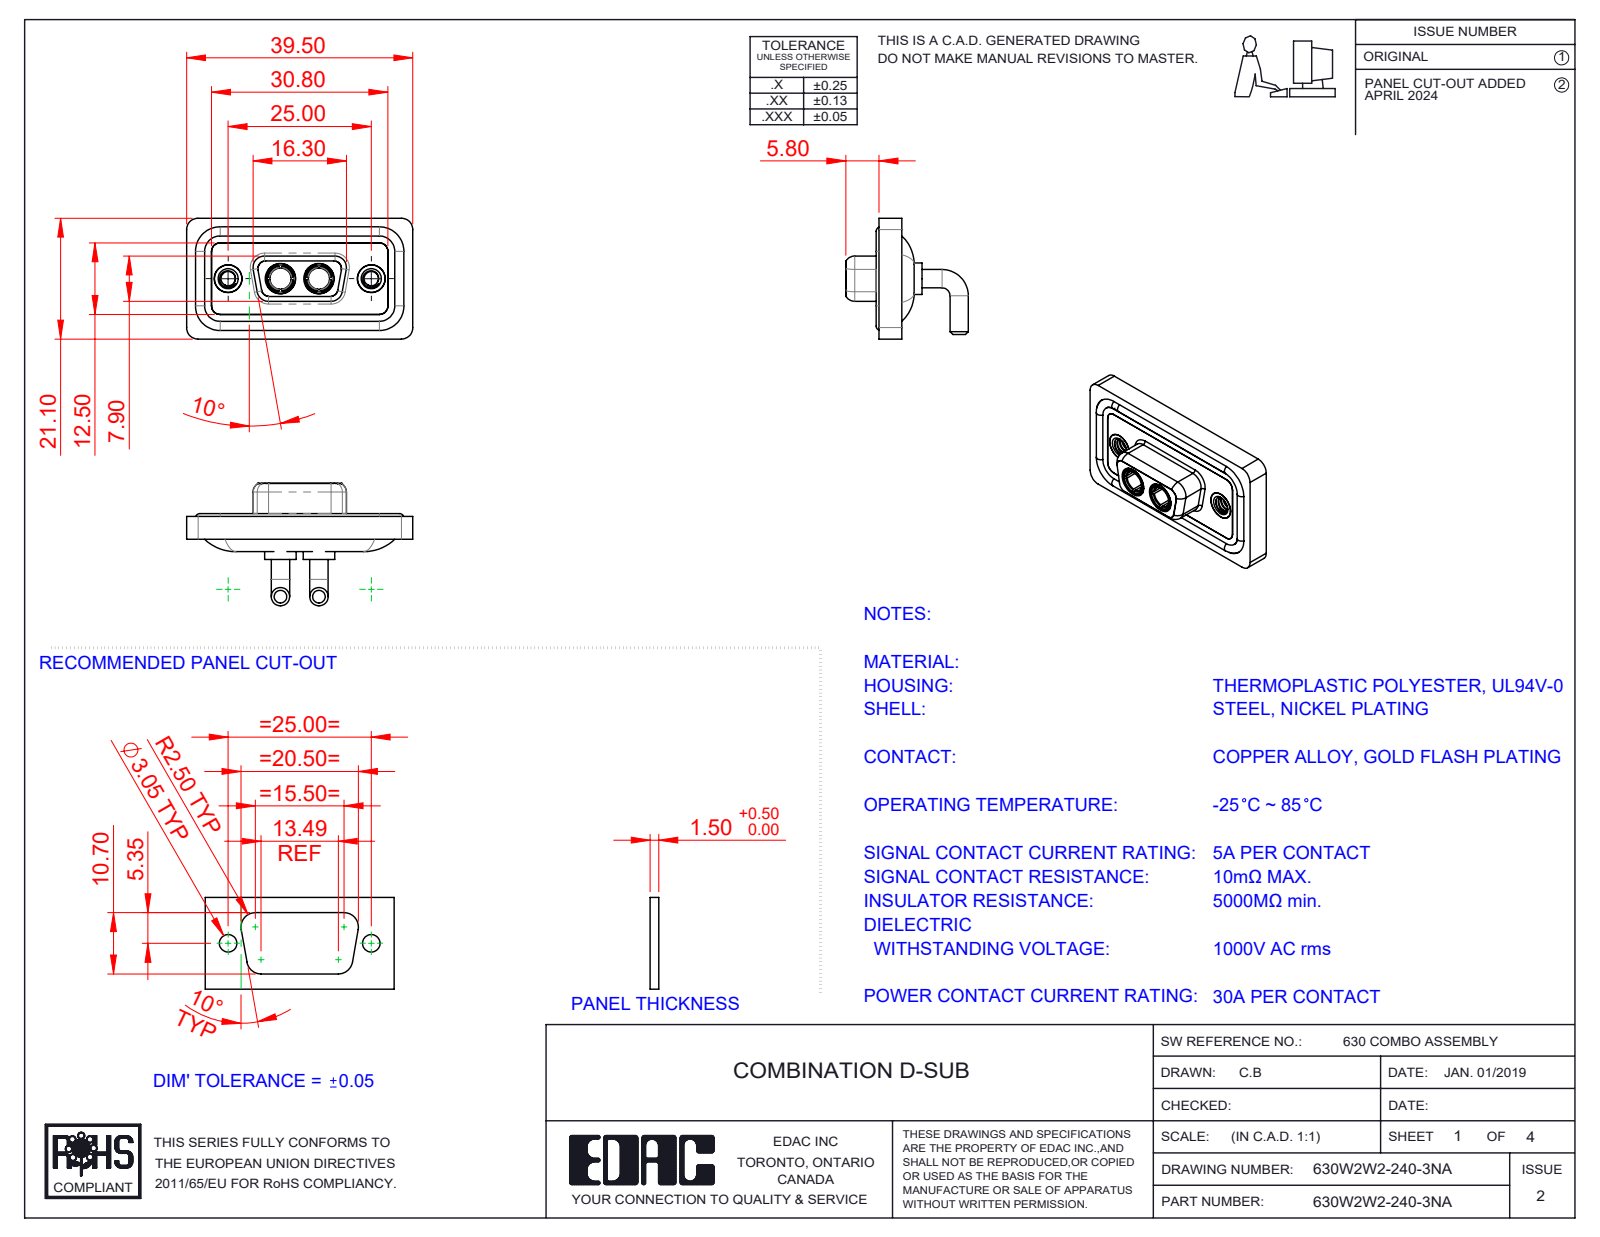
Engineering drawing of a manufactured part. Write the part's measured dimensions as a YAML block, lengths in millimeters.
part_name: "Power Socket_30A RA; 630Combo Shell Front_09 Contacts; 630Combo Threaded Rivet_A; 630Combo Housing_2W2 (+3 more)"
step_written_by: "SolidWorks 2023 (CONFIG_CONTROL_DESIGN)"
units: millimeters
bodies: {solids: 11, faces: 536, planar: 163, cylindrical: 236, other: 137}
overall_size: [39.5, 21.4, 21.1]
volume: 4865
surface_area: 7826
round_holes:
  - {diameter: 4.85, count: 4}
  - {diameter: 2.5, count: 2}
  - {diameter: 3.7, count: 2}
  - {diameter: 4, count: 2}
  - {diameter: 4.05, count: 2}
  - {diameter: 5, count: 2}
  - {diameter: 5.3, count: 2}
round_bosses_or_shafts:
  - {diameter: 3.2, count: 4}
  - {diameter: 1.6, count: 4}
  - {diameter: 5.5, count: 2}
  - {diameter: 5.2, count: 2}
  - {diameter: 4.96, count: 2}
  - {diameter: 4.95, count: 2}
  - {diameter: 4.8, count: 2}
  - {diameter: 4.75, count: 2}
partial_cylinders:
  - {radius: 1.5, count: 18}
  - {radius: 2, count: 18}
  - {radius: 1.35, count: 8}
  - {radius: 1.6, count: 8}
  - {radius: 0.25, count: 4}
  - {radius: 0.5, count: 4}
  - {radius: 0.6, count: 4}
  - {radius: 0.65, count: 4}
face_to_face_distances: [0.4, 1.8, 1.1, 2.9, 2.5, 1.6, 3.1, 1.5, 2.1, 3.7]
hole_center_spacings: [9.14, 15.86, 6.72, 25]
